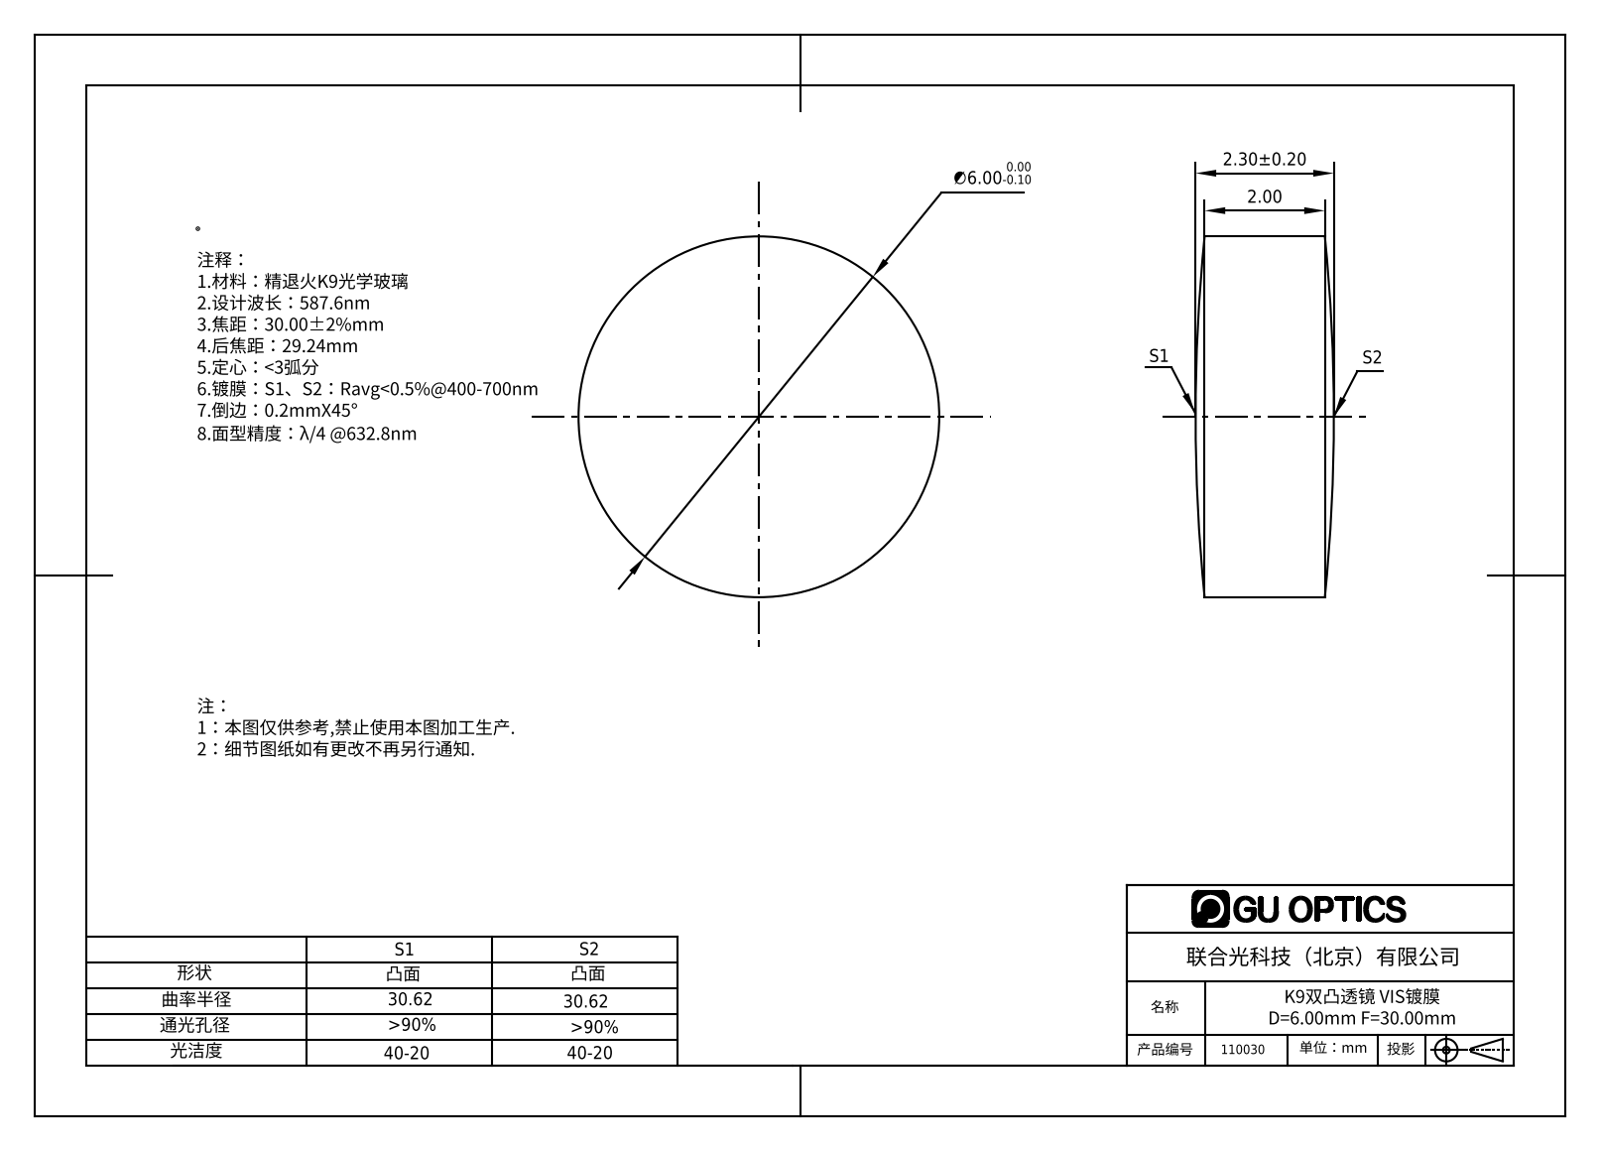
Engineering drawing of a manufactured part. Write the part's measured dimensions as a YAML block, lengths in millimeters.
part_name: "110008"
step_written_by: "SolidWorks 2016 (CONFIG_CONTROL_DESIGN)"
units: millimeters
bodies: {solids: 1, faces: 6, planar: 0, cylindrical: 2, other: 4}
overall_size: [70, 70, 26.83]
volume: 96535
surface_area: 12847
round_bosses_or_shafts:
  - {diameter: 70, count: 1}
